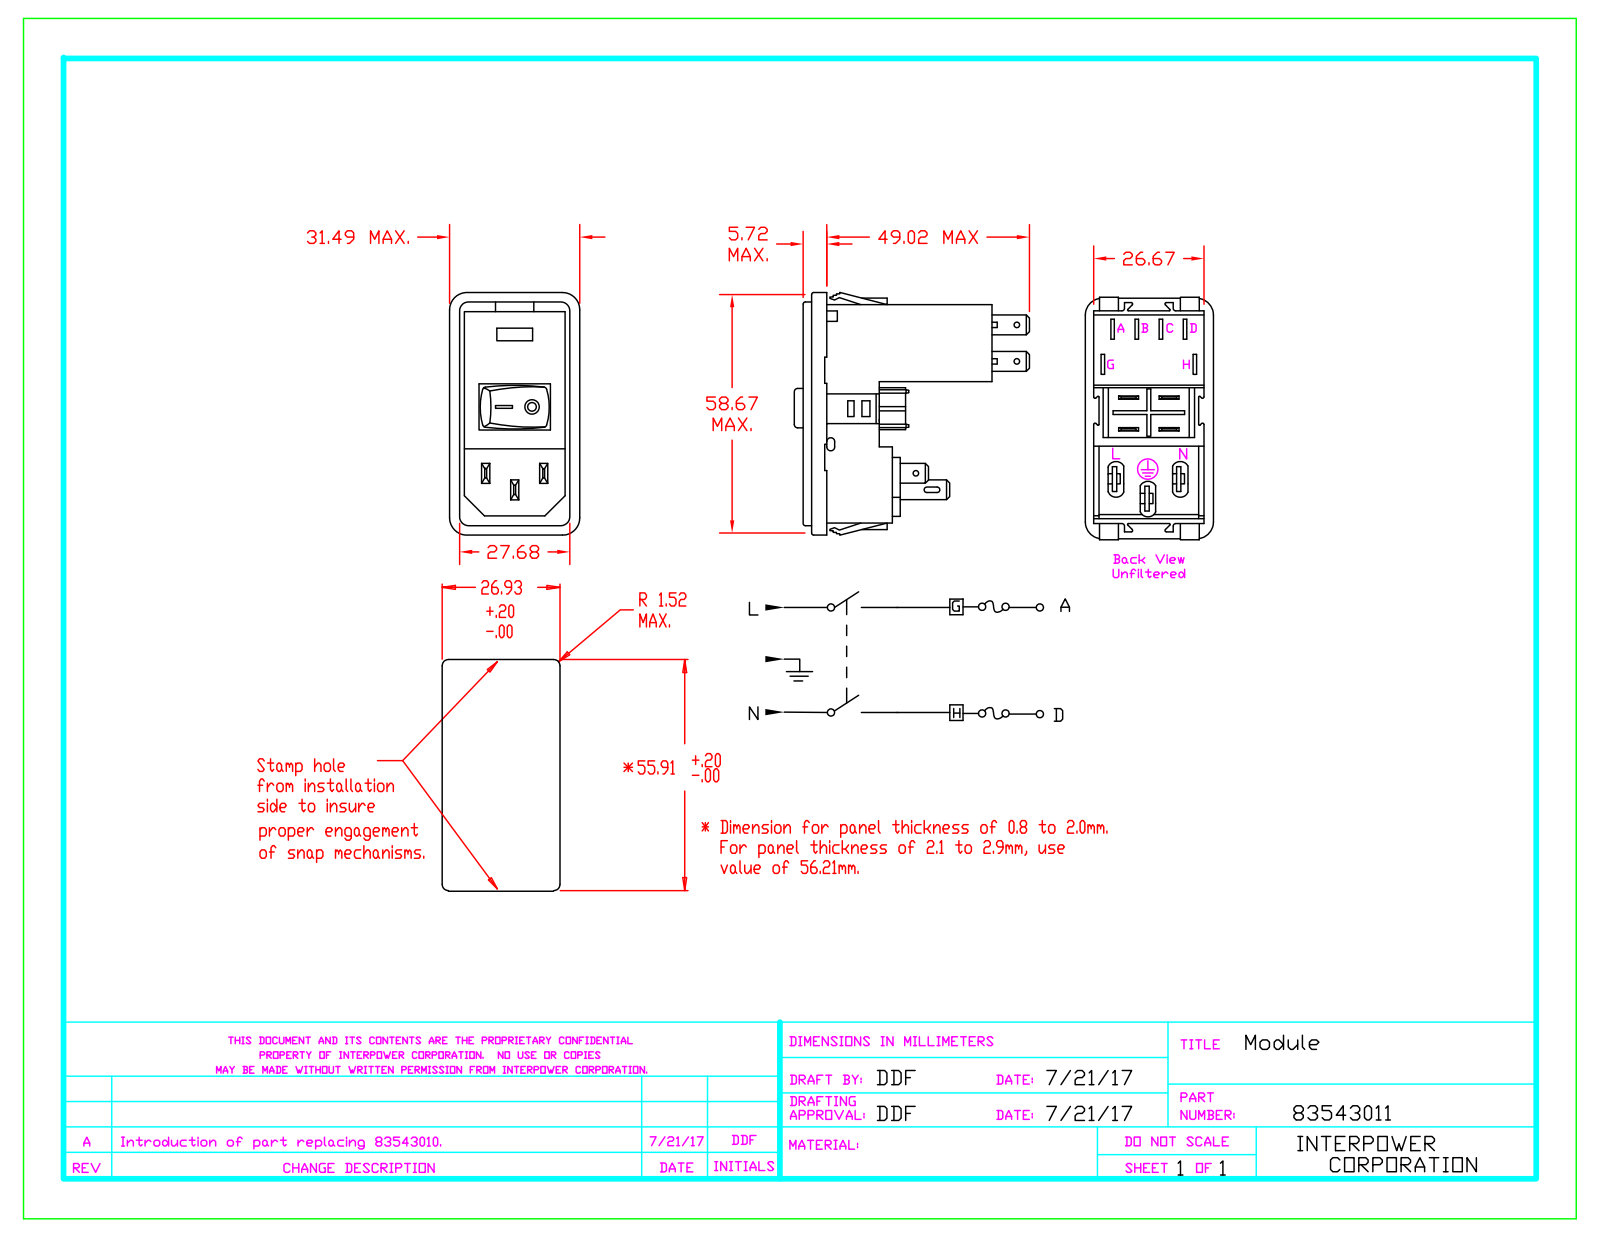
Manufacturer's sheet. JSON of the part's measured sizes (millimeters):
{"part_name": "83543010-R1", "step_written_by": "SolidWorks 2007 (CONFIG_CONTROL_DESIGN)", "units": "millimeters", "bodies": {"solids": 1, "faces": 595, "planar": 461, "cylindrical": 83, "other": 51}, "overall_size": [59.52, 56.71, 31.49], "volume_mm3": 35595, "surface_area_mm2": 16230, "round_holes": [[1.33, 5], [2.25, 1], [3.5, 1]], "round_bosses_or_shafts": [[2.87, 1], [2.75, 1]], "partial_cylinders_radius": [[1, 19], [0.51, 8], [0.25, 5], [2.16, 4], [4.19, 4], [0.67, 2], [0.76, 2], [0.88, 1]], "face_to_face_distances": [26, 18.65, 0.48, 12.7, 5.71, 16.25, 39.96, 45.67, 34.9, 25.74], "hole_center_spacings": [8.82, 10.6, 36.48, 43.43]}
